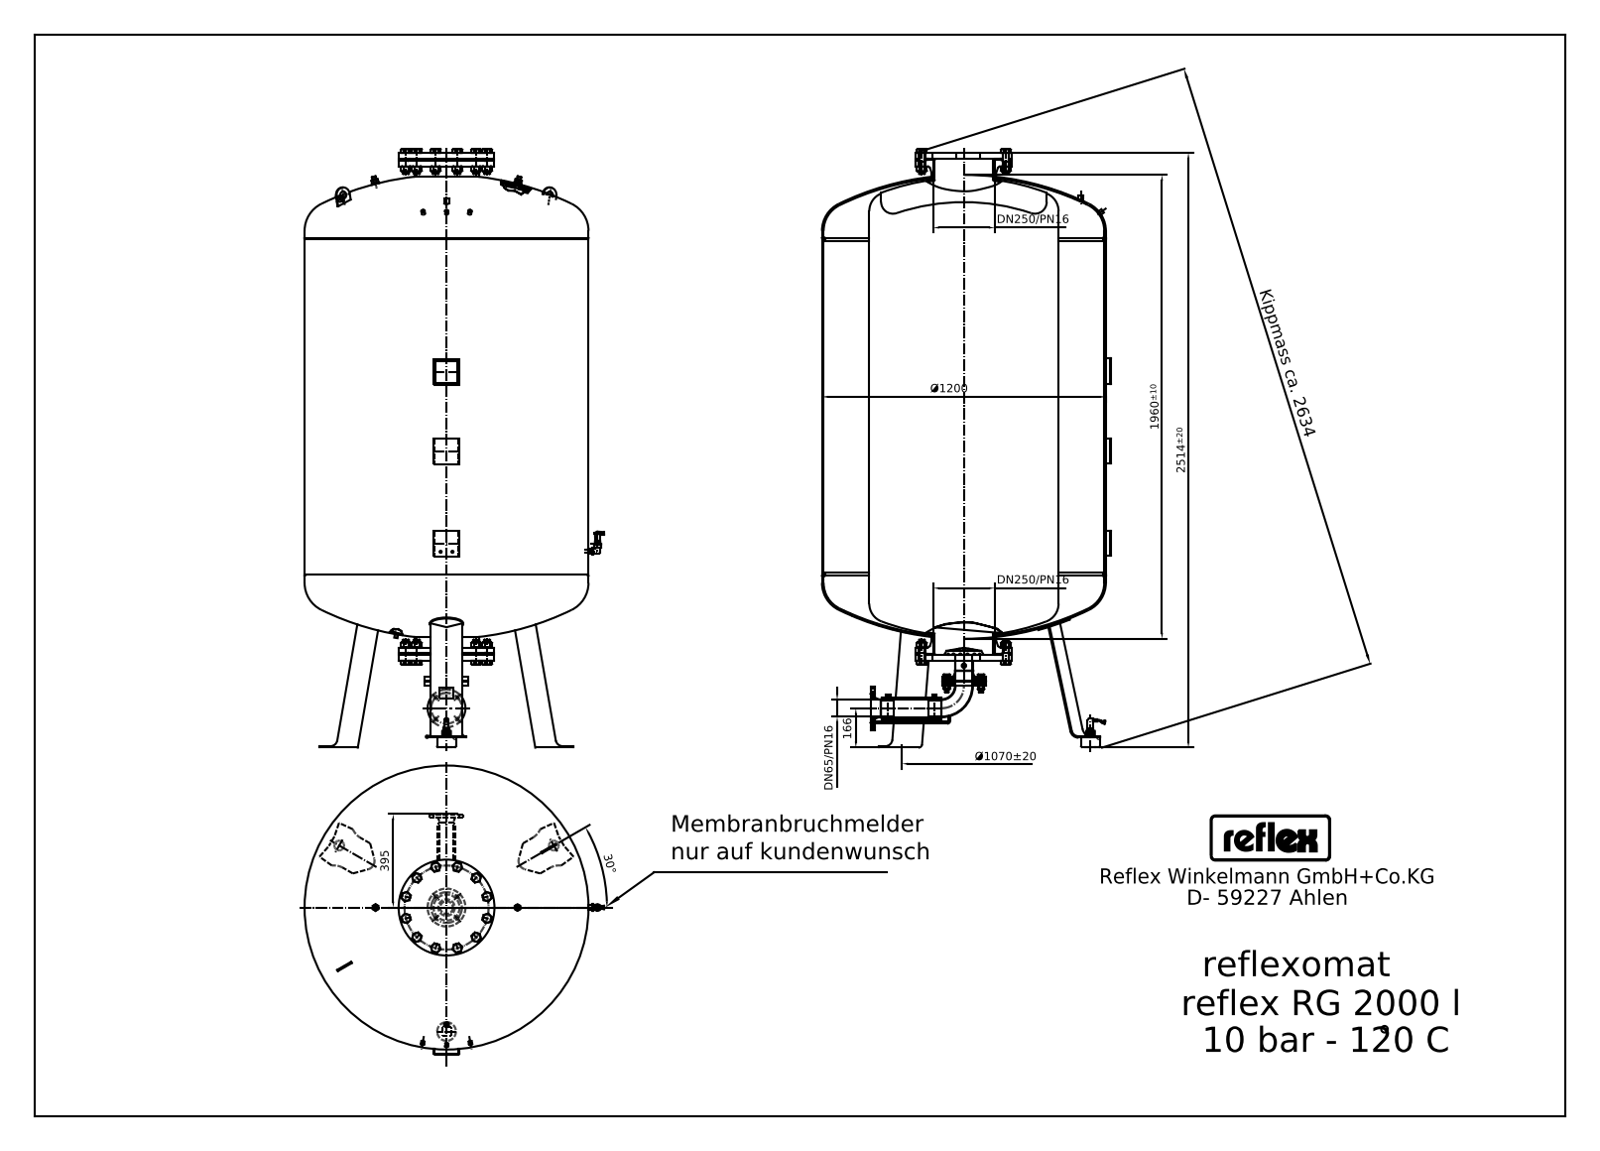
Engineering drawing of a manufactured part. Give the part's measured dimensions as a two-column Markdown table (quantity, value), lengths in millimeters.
| quantity | value |
| --- | --- |
| STEP written by | Mechanical Desktop 2009 (CONFIG_CONTROL_DESIGN) |
| units | millimeters |
| bodies | 33 solids, 1189 faces (677 planar, 280 cylindrical, 232 other) |
| overall size | 2510 × 1266 × 1220 |
| volume | 2 048 000 000 mm³ |
| surface area | 15 380 000 mm² |
| round holes (diameter × count) | 9 × 2, 11.45 × 2, 3.5 × 1, 8 × 1, 14.95 × 1, 30 × 1, 260.4 × 1 |
| round bosses / shafts (diameter × count) | 16 × 12, 12 × 4, 21.3 × 3, 18.5 × 3, 76.1 × 2, 28 × 2, 20 × 2, 10 × 2 |
| partial cylindrical surfaces (radius × count) | 25 × 18, 2 × 10, 1 × 5, 8.44 × 4, 3.38 × 3, 6 × 3, 3 × 2, 5.76 × 2 |
| main face-to-face distances | 1450, 22, 2095, 27, 2068, 335, 1763, 313, 2117, 1785 |
| hole center spacings | 720.43, 50, 495, 619.5, 792.97, 1593.84, 1609.45, 2296.5 |
